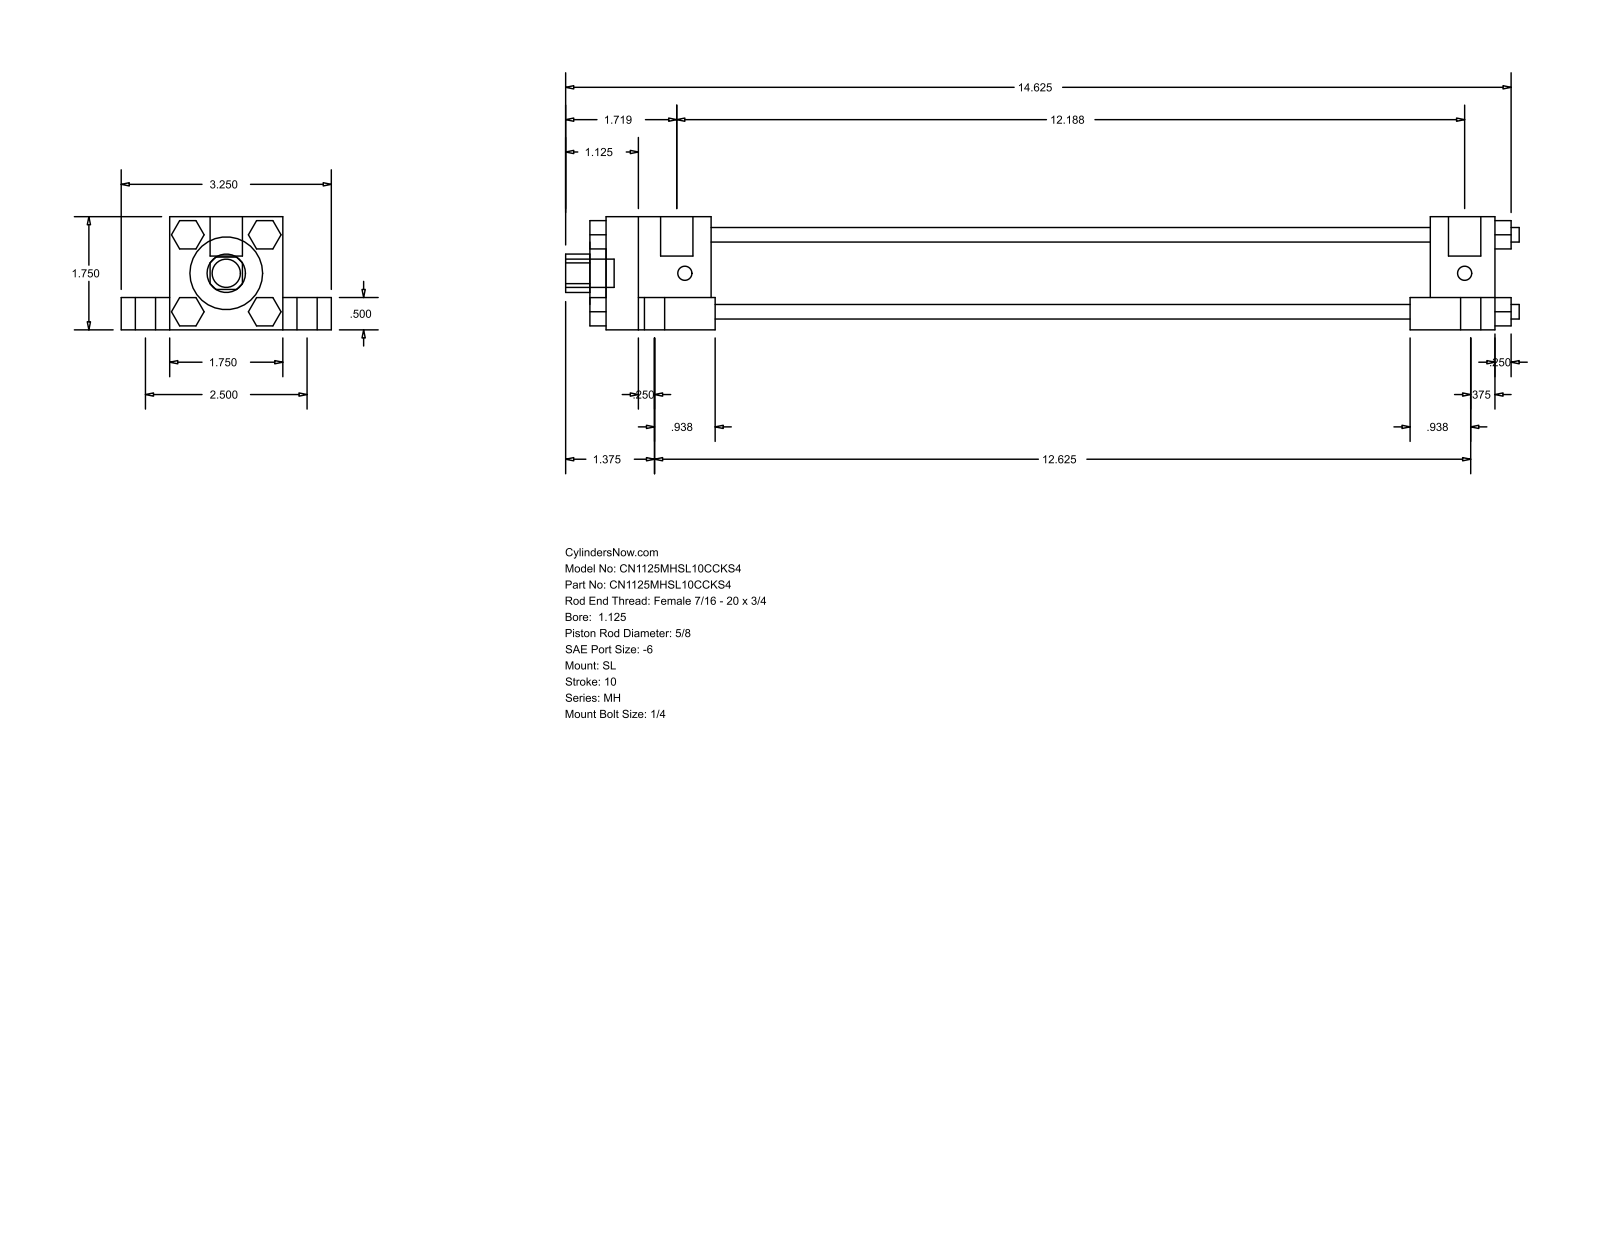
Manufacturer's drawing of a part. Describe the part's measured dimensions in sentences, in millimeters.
The part is named "MH_SL__0112_0.625". Its 3-D file was written by "GSSL Pune (CONFIG_CONTROL_DESIGN)". It is 0 solids with 150 faces: 114 planar, 36 cylindrical and 0 other. Overall it measures 374.65 by 82.55 by 44.45 millimeters. Round holes: 1 of diameter 15.88, 1 of diameter 28.57, 1 of diameter 34.92. Round bosses or shafts: 4 of diameter 14.29, 4 of diameter 7.94, 4 of diameter 5.71, 4 of diameter 5.56, 2 of diameter 12.7, 1 of diameter 11.11. Partial cylindrical surfaces (rounded edges, fillets, slot ends): 1 of radius 7.54. The main face-to-face distances are 44.46, 19.04, 12.7, 31.76, 63.5, 11.11, 282.58, 307.97, 25.39, 41.27.
